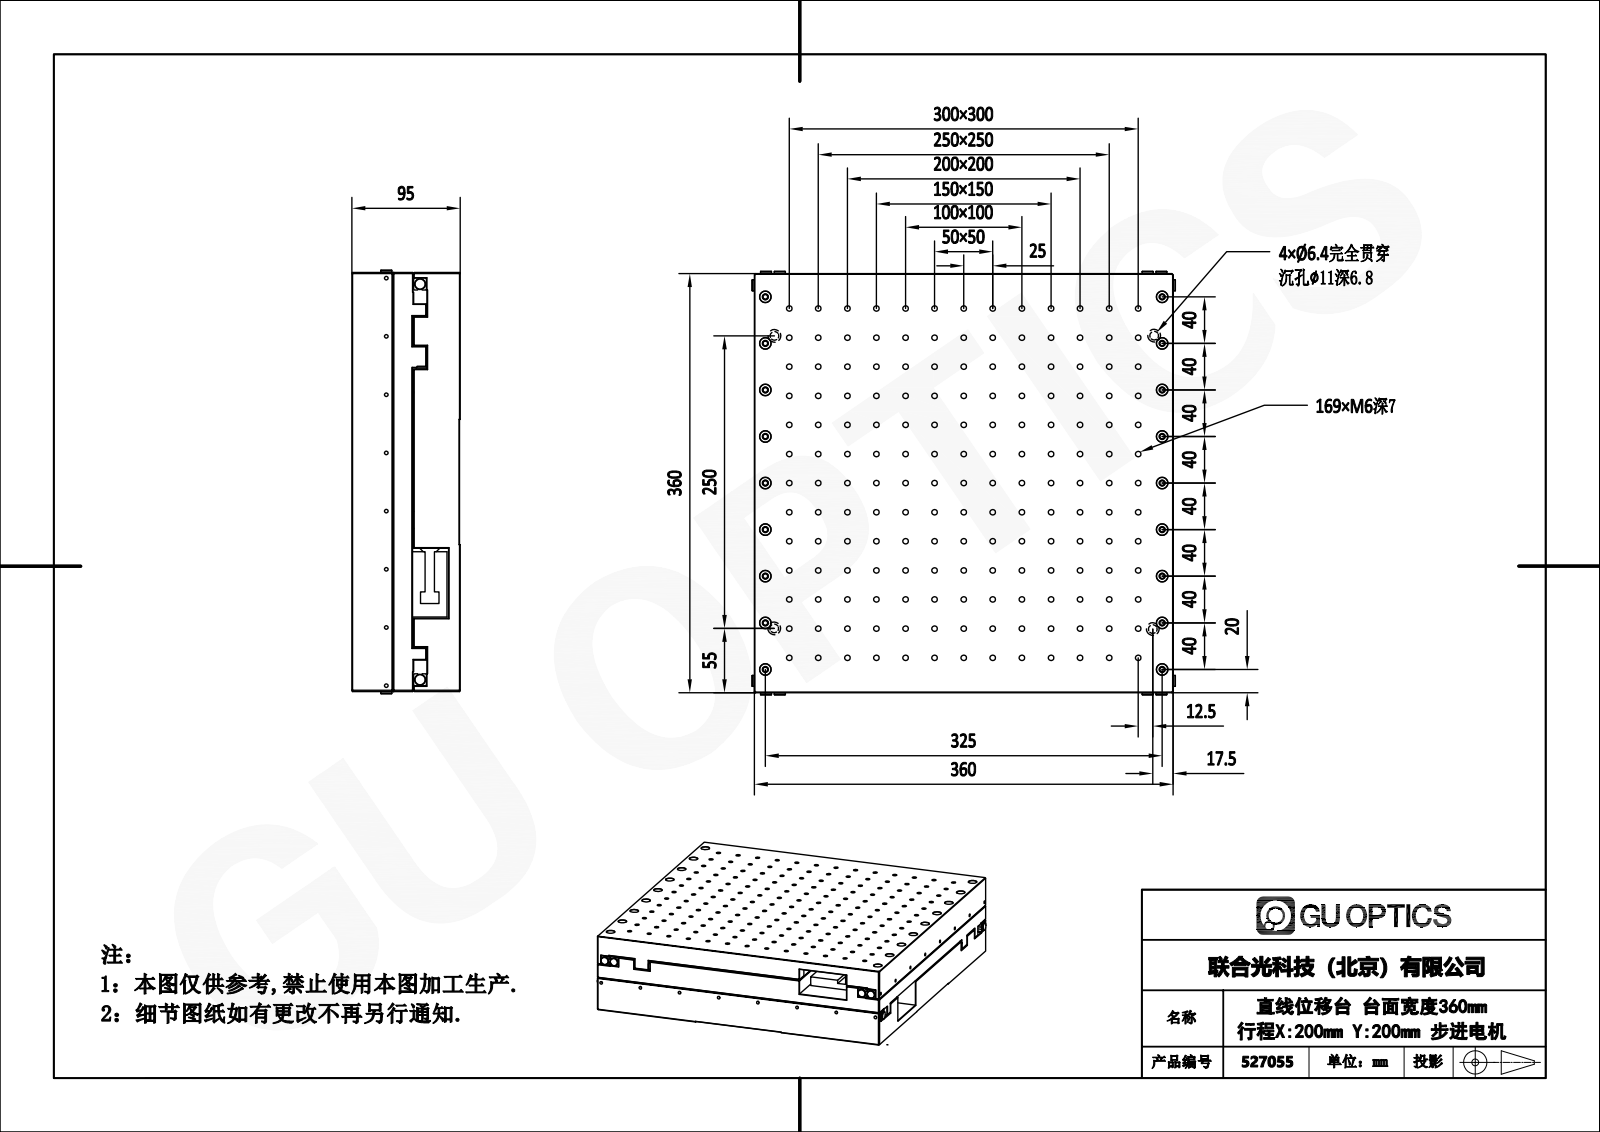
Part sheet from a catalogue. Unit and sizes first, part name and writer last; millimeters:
Units: millimetres
Overall size (bounding box): 364 × 364 × 93
Round holes (diameter × count): ⌀5 ×173, ⌀3.3 ×67, ⌀8 ×64, ⌀4.3 ×54, ⌀5.3 ×36, ⌀10 ×36, ⌀2 ×16, ⌀2.5 ×16, ⌀4.8 ×10, ⌀3.35 ×8, ⌀3.5 ×8, ⌀6 ×8
Round bosses / shafts (diameter × count): ⌀9.5 ×6
Partial cylindrical surfaces — rounded edges, fillets, slot ends (radius × count): R2.5 ×42, R5 ×31, R1 ×4, R125 ×4
Main face-to-face distances: 29, 1, 52, 30, 28, 0.5, 42, 23, 40.5, 41
Hole centre spacings: 40, 200, 343.34, 50, 80, 350.26, 120, 100
Volume: 10 050 000 mm³ · Surface area: 1 451 000 mm²
Bodies: 23 solids, 2626 faces (1063 planar, 1192 cylindrical, 371 other)
STEP written by: SolidWorks 2020 (AUTOMOTIVE_DESIGN)
